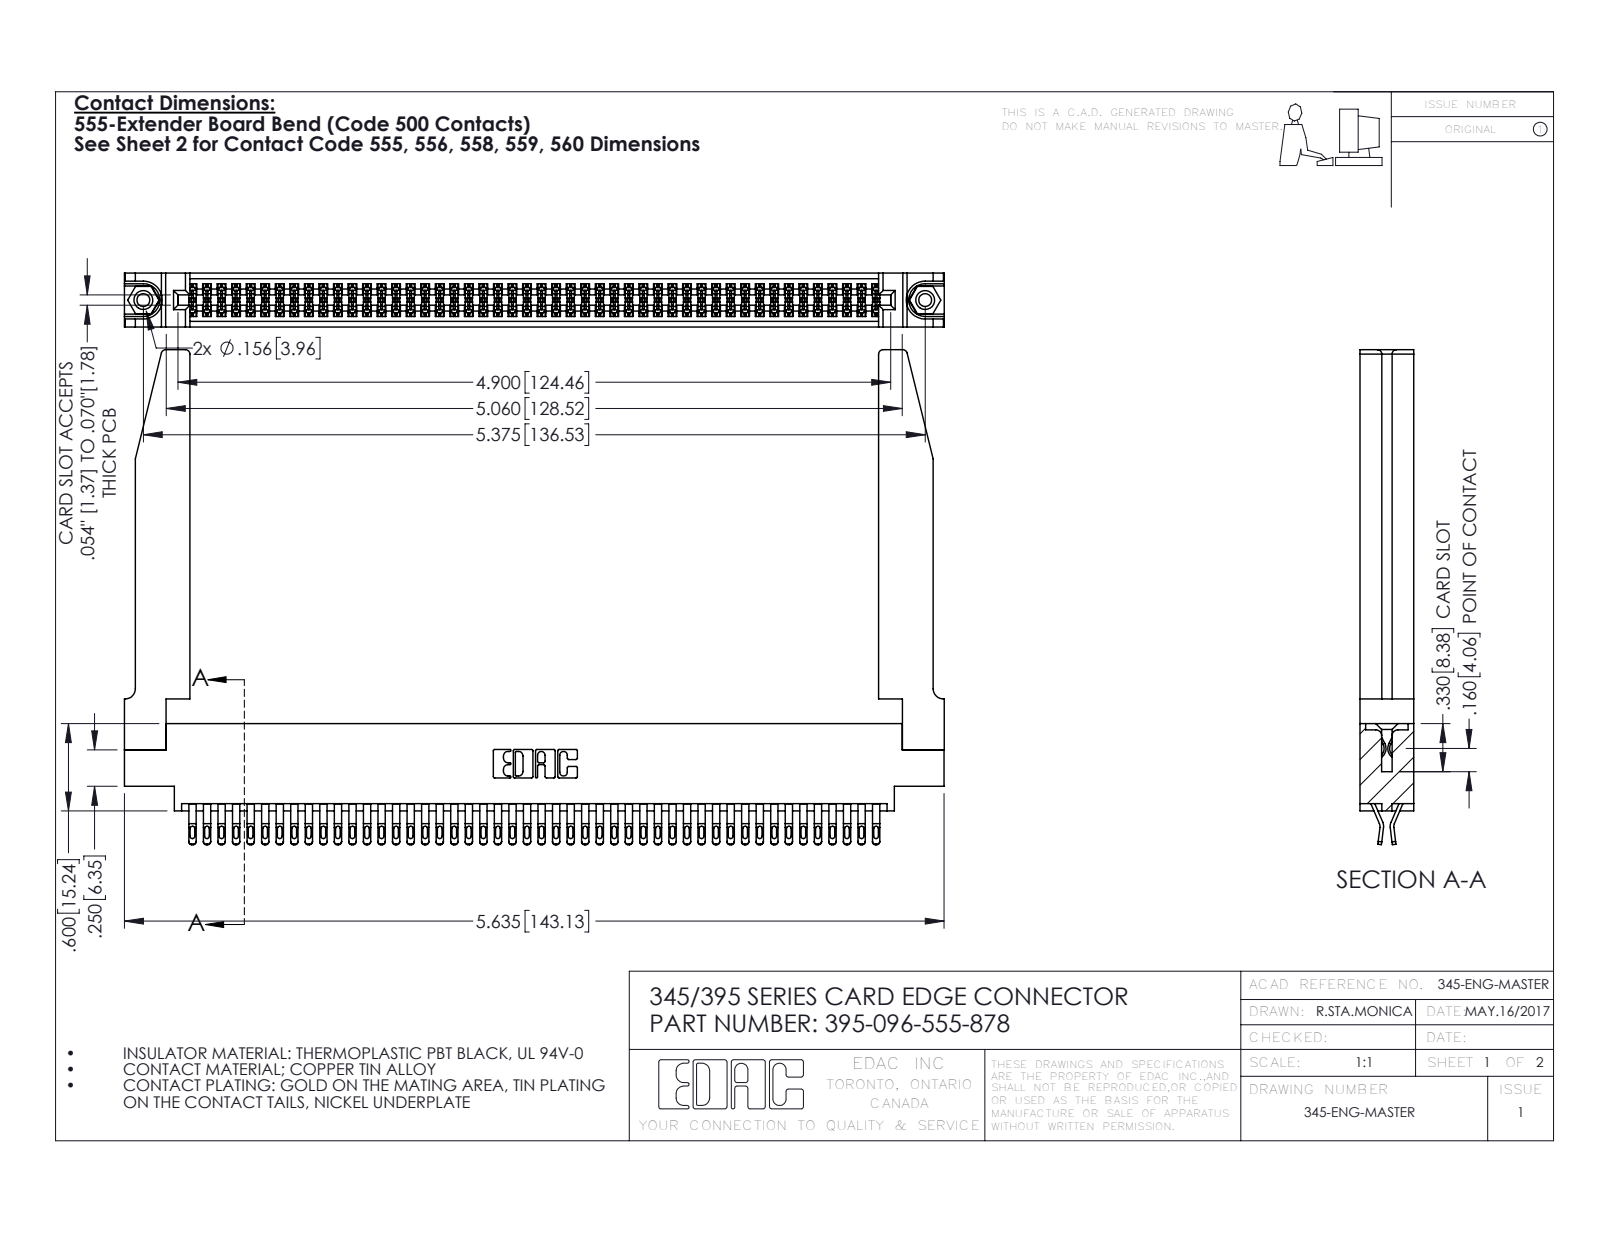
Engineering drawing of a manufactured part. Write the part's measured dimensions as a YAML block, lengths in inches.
part_name: "345-250-001_345-250-001-102; 345-292-001_555 Tail; 395-096-555-878; 345 Part_0.170 Offset - 0.156 Dia-TH (+1 more)"
step_written_by: "SolidWorks 2016 (CONFIG_CONTROL_DESIGN)"
units: inches
bodies: {solids: 101, faces: 5740, planar: 3202, cylindrical: 2486, other: 52}
overall_size: [5.636, 3.402, 0.37]
volume: 1.336
surface_area: 44.87
round_holes:
  - {diameter: 0.089, count: 2}
  - {diameter: 0.125, count: 2}
  - {diameter: 0.156, count: 2}
  - {diameter: 0.064, count: 1}
round_bosses_or_shafts:
  - {diameter: 0.155, count: 2}
partial_cylinders:
  - {radius: 0.016, count: 240}
  - {radius: 0.02, count: 192}
  - {radius: 0.006, count: 144}
  - {radius: 0.01, count: 22}
  - {radius: 0.03, count: 8}
  - {radius: 0.007, count: 6}
  - {radius: 0.031, count: 6}
  - {radius: 0.026, count: 3}
face_to_face_distances: [0.37, 0.072, 0.298, 0.025, 0.098, 0.272, 0.2, 0.225, 0.175, 0.15]
hole_center_spacings: [0.27, 5.139, 5.375]
